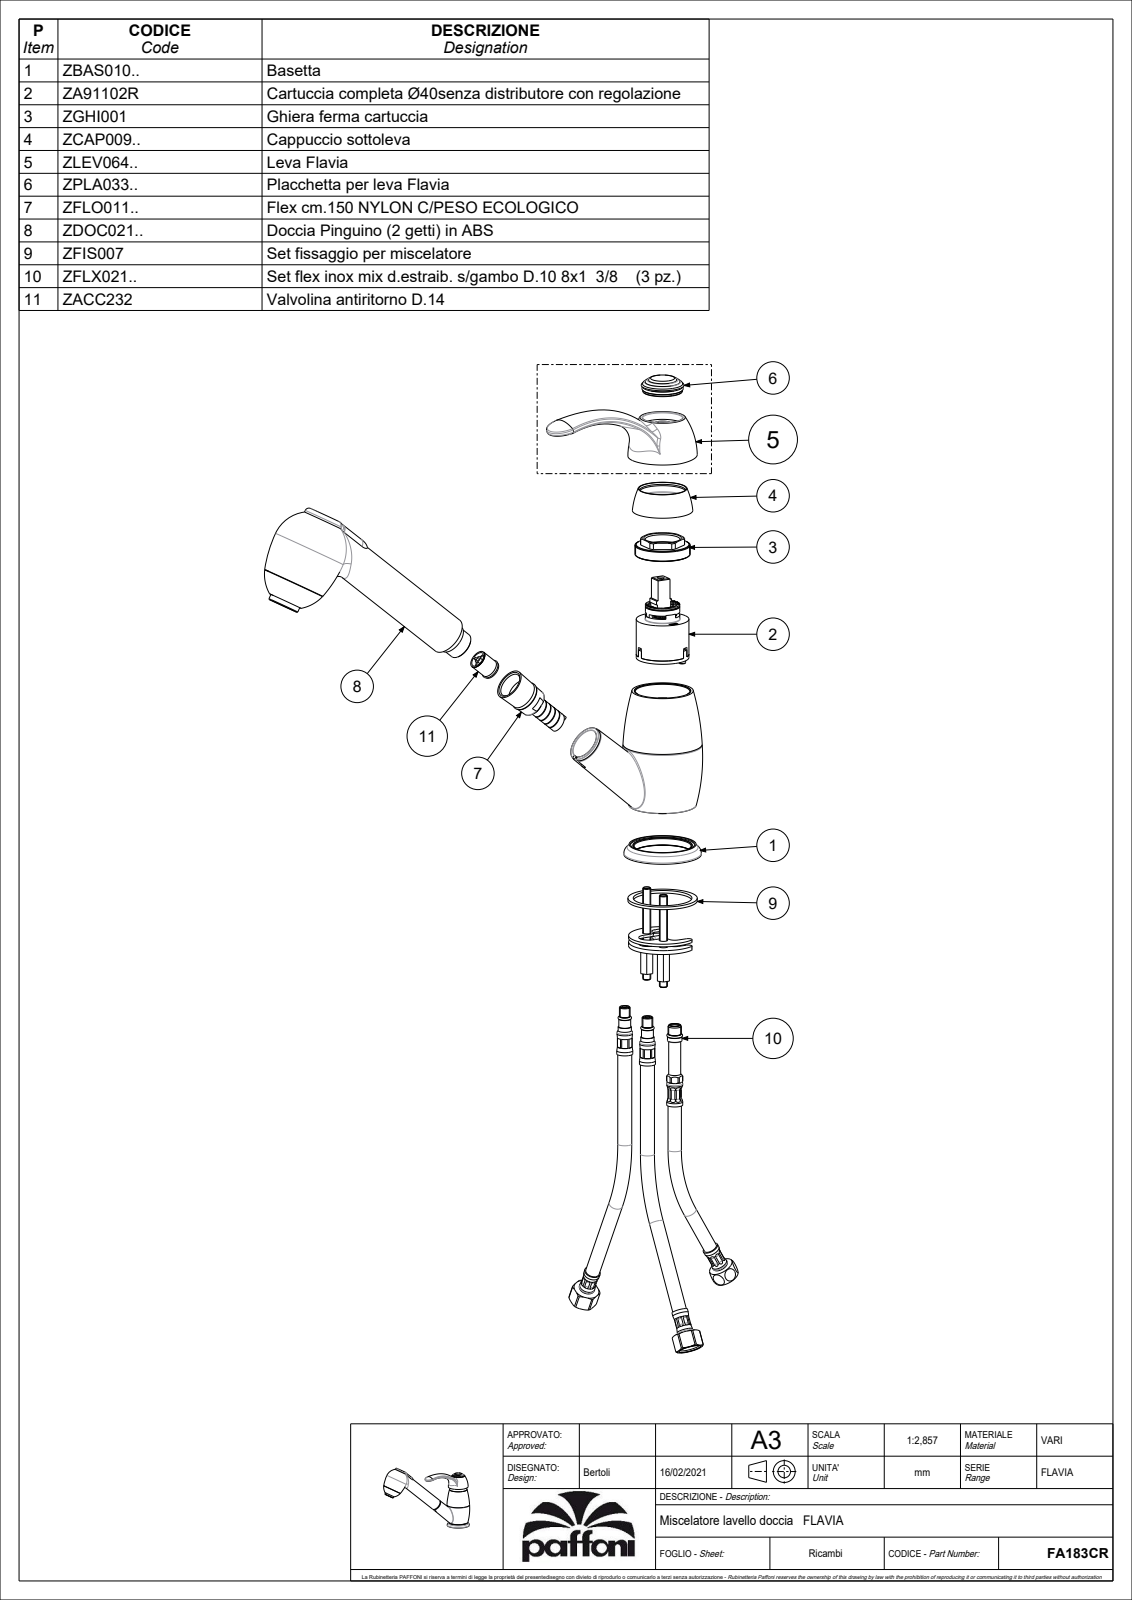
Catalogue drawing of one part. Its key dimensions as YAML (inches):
part_name: "FA183CR"
step_written_by: "CREO PARAMETRIC BY PTC INC, 2020044 (CONFIG_CONTROL_DESIGN)"
units: inches
bodies: {solids: 1, faces: 1761, planar: 939, cylindrical: 515, other: 307}
overall_size: [9.926, 7.044, 2.364]
volume: 25.75
surface_area: 221.2
round_holes:
  - {diameter: 0.039, count: 104}
  - {diameter: 0.276, count: 6}
  - {diameter: 0.157, count: 2}
  - {diameter: 0.217, count: 2}
  - {diameter: 0.315, count: 2}
  - {diameter: 0.339, count: 2}
  - {diameter: 0.37, count: 2}
  - {diameter: 0.433, count: 2}
  - {diameter: 0.461, count: 2}
  - {diameter: 0.827, count: 2}
  - {diameter: 0.118, count: 1}
  - {diameter: 0.13, count: 1}
round_bosses_or_shafts:
  - {diameter: 2.283, count: 1}
  - {diameter: 2.028, count: 1}
  - {diameter: 1.89, count: 1}
  - {diameter: 1.799, count: 1}
  - {diameter: 1.76, count: 1}
  - {diameter: 1.732, count: 1}
  - {diameter: 1.654, count: 1}
  - {diameter: 1.63, count: 1}
partial_cylinders:
  - {radius: 0.02, count: 26}
  - {radius: 0.008, count: 24}
  - {radius: 0.059, count: 4}
  - {radius: 0.315, count: 2}
  - {radius: 0.492, count: 2}
  - {radius: 0.098, count: 1}
  - {radius: 0.276, count: 1}
  - {radius: 0.396, count: 1}
face_to_face_distances: [0.02, 0.098, 0.039, 0.256, 1.35, 1.201, 0.236, 0.028, 0.528, 0.508]
hole_center_spacings: [0.334, 0.334, 0.139, 0.07, 0.272, 0.541, 0.61, 0.206]
